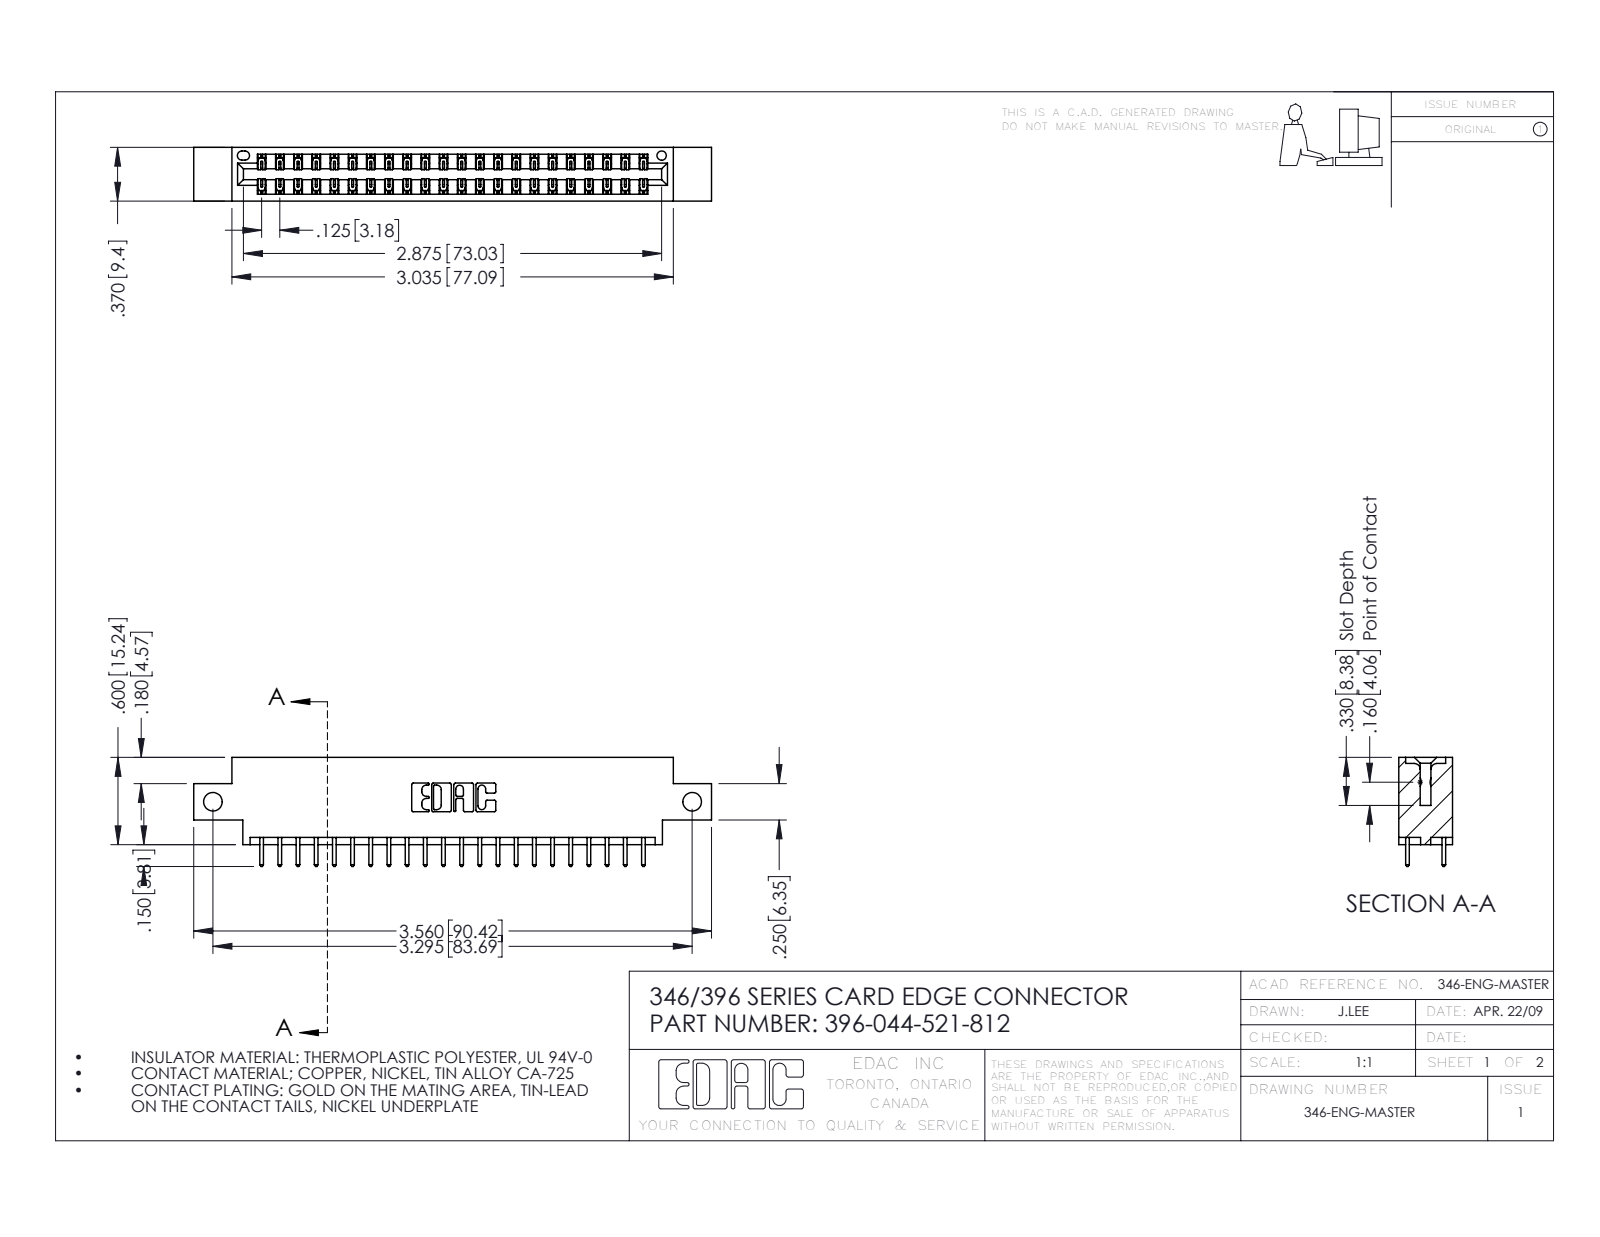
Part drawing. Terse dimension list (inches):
name: 346 Part_0.170 Offset - Side Mount; 396-044-521-812; 345-292-001_345-293-121
written by: SolidWorks 2016 (CONFIG_CONTROL_DESIGN)
unit: in
bodies: 45 solids, 2414 faces (1620 planar, 794 cylindrical, 0 other)
size: 3.56 × 0.75 × 0.37
volume: 0.513 in³; area: 17.29 in²
holes: 2× ⌀0.128, 1× ⌀0.064
rounds: 66× R0.006, 44× R0.01, 22× R0.01, 6× R0.007, 6× R0.031, 3× R0.026, 2× R0.014, 2× R0.022
face distances: 0.048, 0.322, 0.37, 0.25, 0.072, 0.298, 0.025, 0.275, 0.148, 0.222
hole spacings: 3.295
